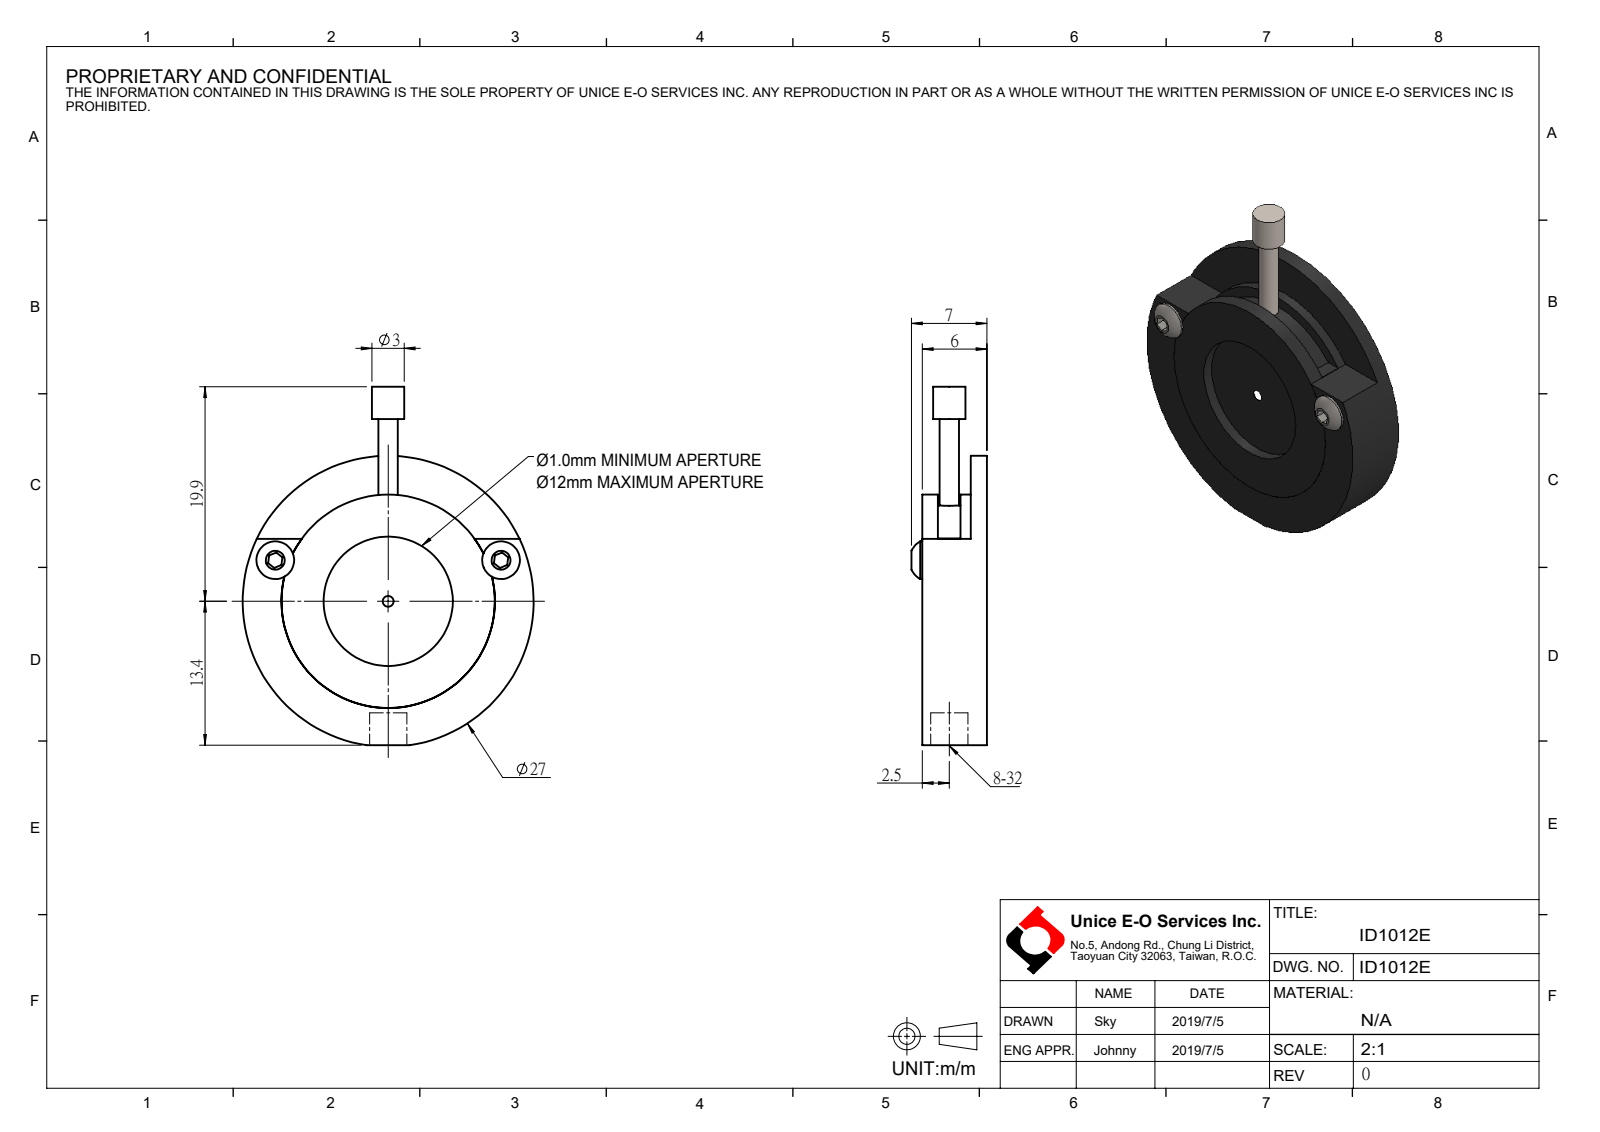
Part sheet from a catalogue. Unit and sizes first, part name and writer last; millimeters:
Units: millimetres
Overall size (bounding box): 33.25 × 27 × 7
Round holes (diameter × count): ⌀1 ×1, ⌀3.45 ×1, ⌀12 ×1, ⌀17 ×1, ⌀17.8 ×1, ⌀19.8 ×1
Round bosses / shafts (diameter × count): ⌀3.5 ×2, ⌀27 ×1, ⌀3 ×1, ⌀1.8 ×1
Main face-to-face distances: 6, 2, 4, 3, 5, 1, 4.9, 2.9, 1.1, 1.5
Bodies: 0 solids, 62 faces (30 planar, 28 cylindrical, 4 other)
Part name (STEP PRODUCT): ID1012E
STEP written by: SolidWorks 2016 (AUTOMOTIVE_DESIGN)
